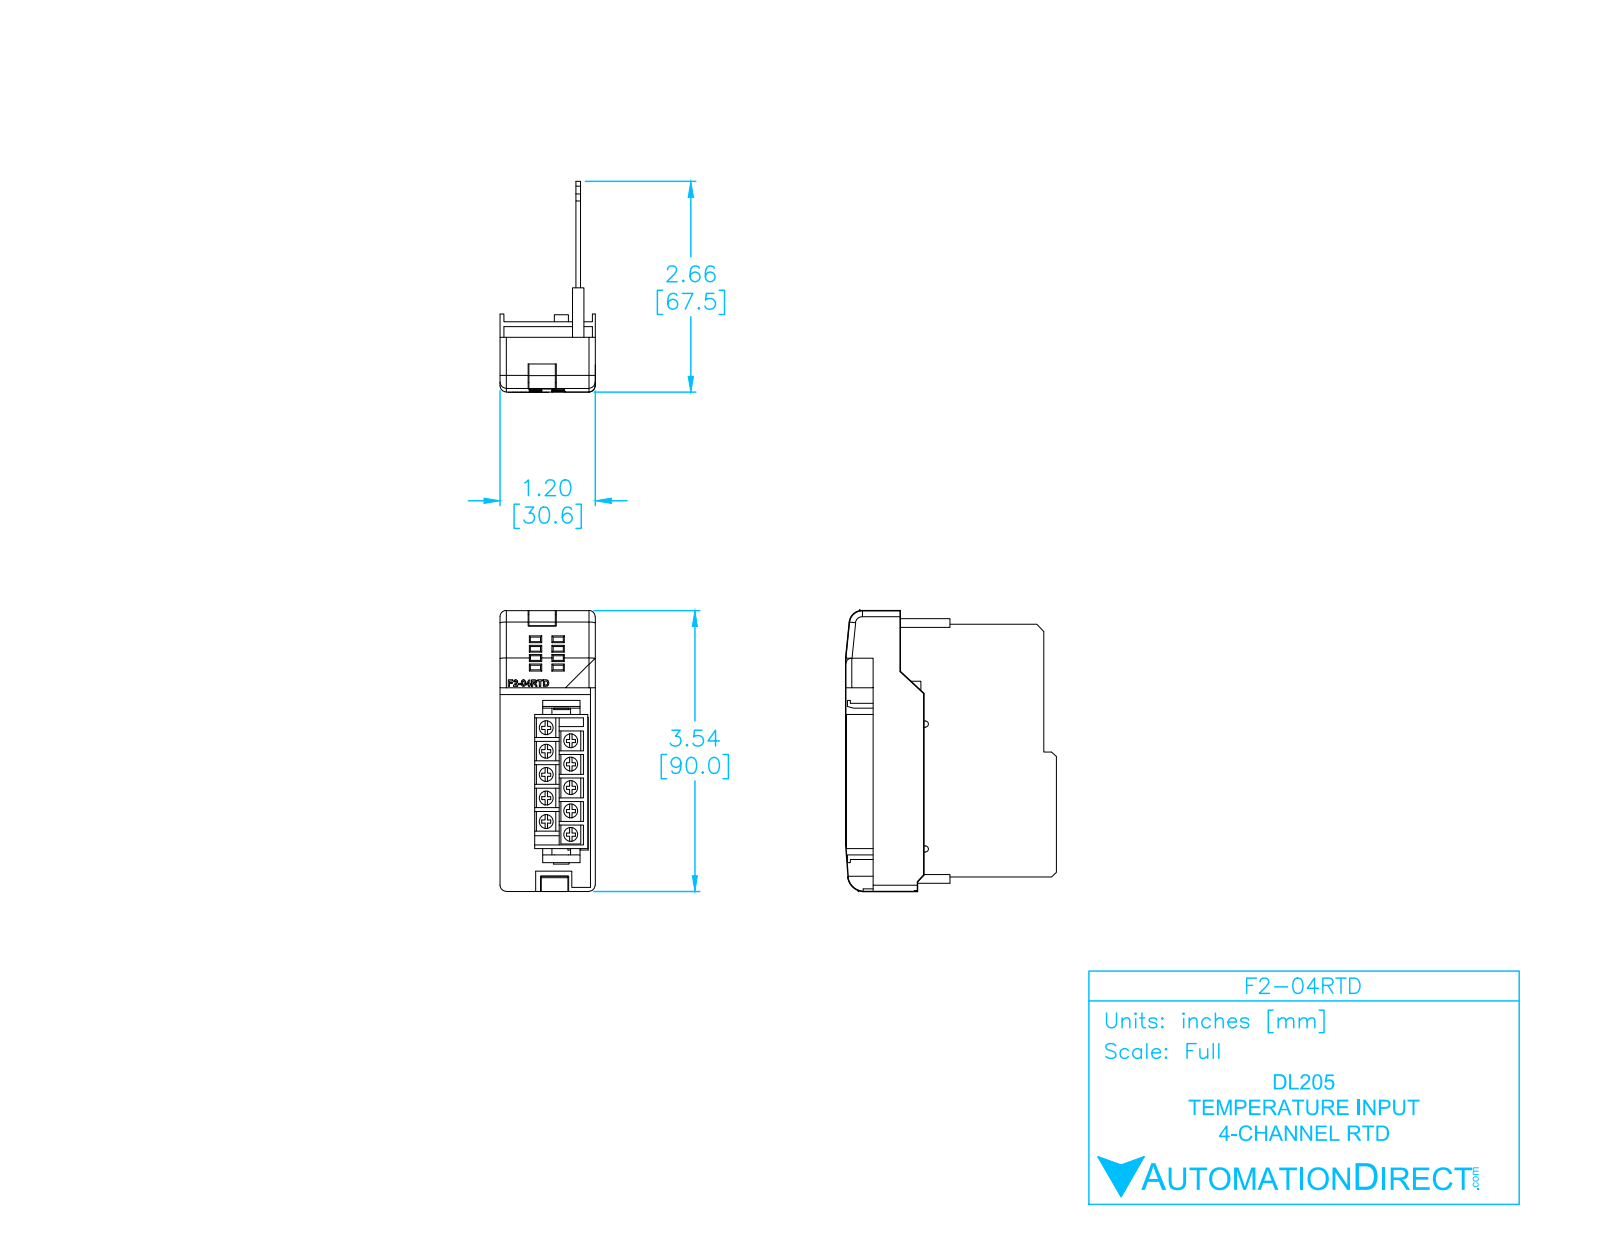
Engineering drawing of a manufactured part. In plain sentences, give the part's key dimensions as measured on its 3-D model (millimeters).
The part is named "F2-04RTD_ModuleCase_light_NEW". Its 3-D file was written by "SolidWorks 2009 (AUTOMOTIVE_DESIGN)". It is 6 solids with 579 faces: 423 planar, 75 cylindrical and 81 other. Overall it measures 90 by 67.56 by 30.55 millimeters. Its volume is 25 374 cubic millimeters and its surface area 28 532 square millimeters. Round bosses or shafts: 10 of diameter 4.5. Partial cylindrical surfaces (rounded edges, fillets, slot ends): 16 of radius 0.35, 9 of radius 2, 2 of radius 0.25, 2 of radius 1, 2 of radius 1.25, 1 of radius 4.12, 1 of radius 5.39. The main face-to-face distances are 1.5, 4.72, 6.22, 2.37, 3.87, 2.35, 3.22, 0.85, 7.25, 8.14.
